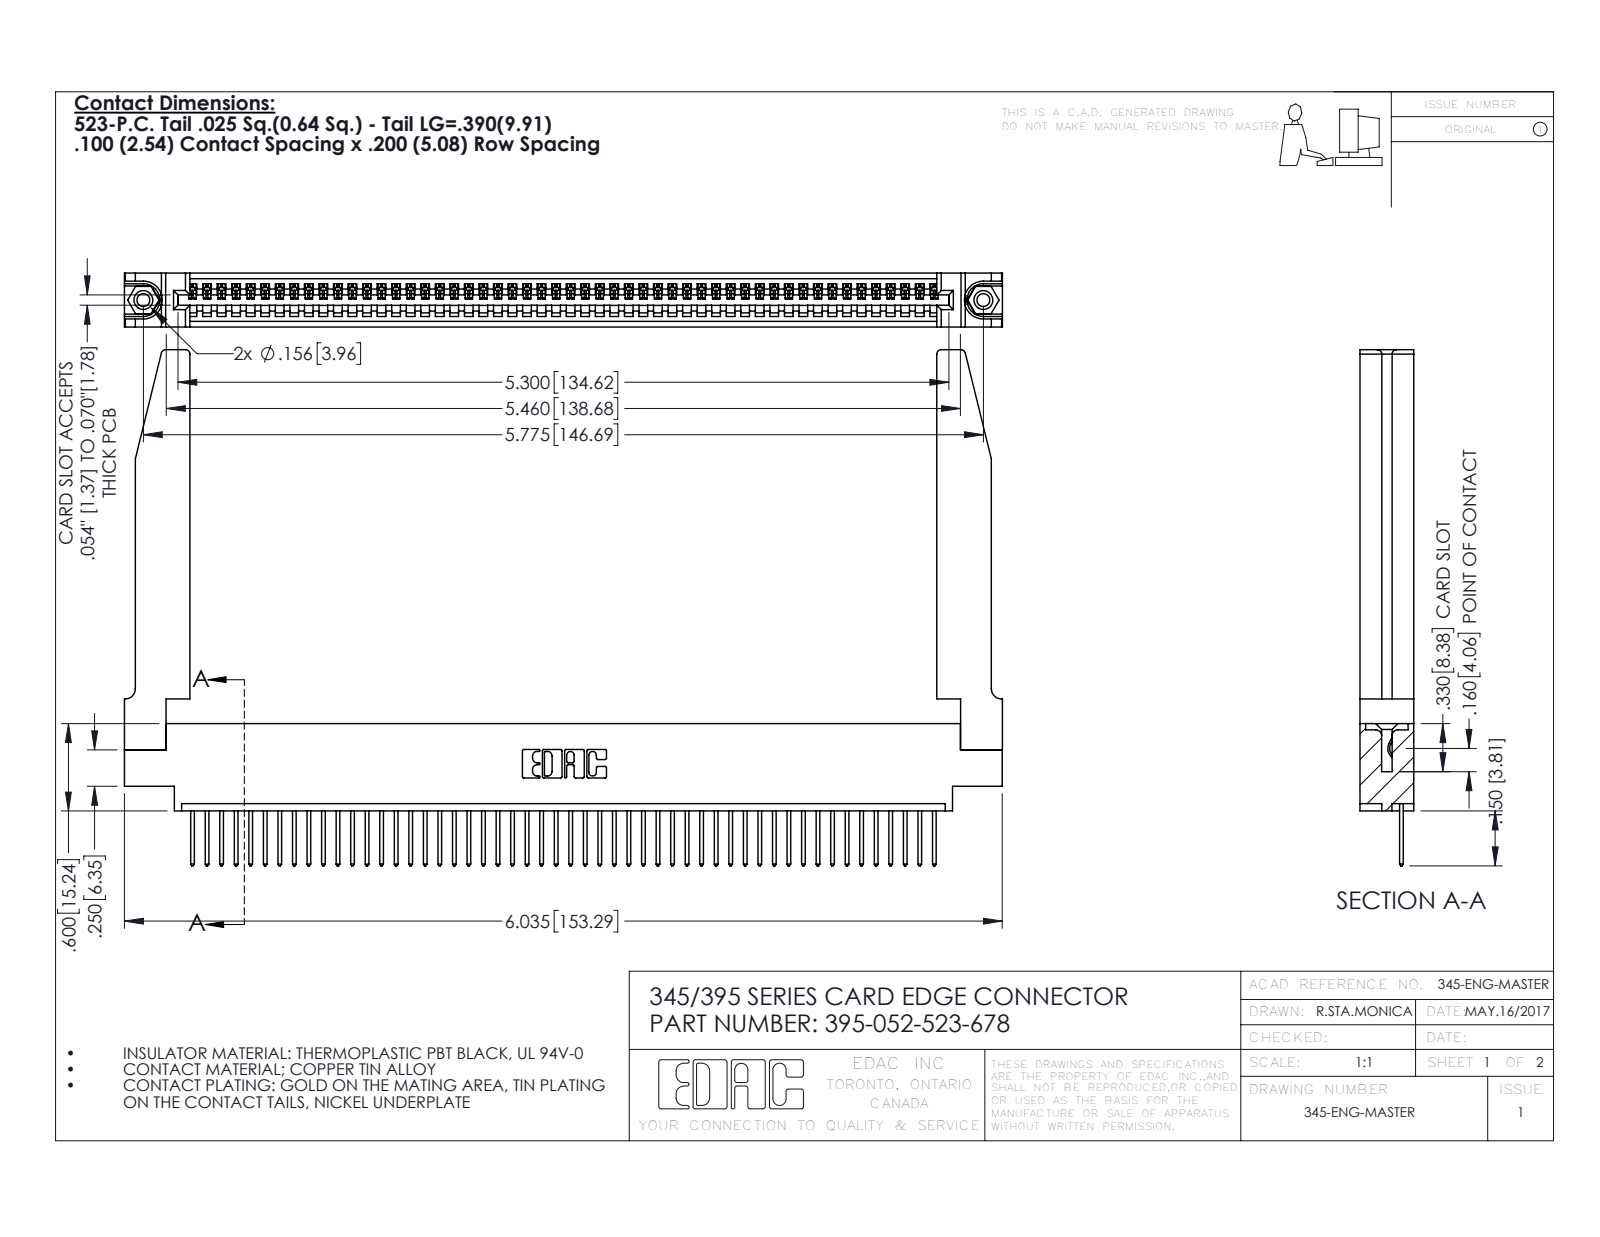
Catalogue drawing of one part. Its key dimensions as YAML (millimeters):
part_name: "395-052-523-678; 345-250-001_345-250-001-102; 345-220-078_345-220-078; 345-292-001_345-293-123 (+1 more)"
step_written_by: "SolidWorks 2016 (CONFIG_CONTROL_DESIGN)"
units: millimeters
bodies: {solids: 57, faces: 3380, planar: 2306, cylindrical: 1022, other: 52}
overall_size: [153.3, 90.1, 9.4]
volume: 22290
surface_area: 26450
round_holes:
  - {diameter: 2.3, count: 2}
  - {diameter: 3.2, count: 2}
  - {diameter: 4, count: 2}
  - {diameter: 1.6, count: 1}
round_bosses_or_shafts:
  - {diameter: 3.9, count: 2}
partial_cylinders:
  - {radius: 0.2, count: 104}
  - {radius: 0.3, count: 104}
  - {radius: 0.3, count: 22}
  - {radius: 0.8, count: 8}
  - {radius: 0.2, count: 6}
  - {radius: 0.8, count: 6}
  - {radius: 0.7, count: 3}
  - {radius: 0.8, count: 2}
face_to_face_distances: [9.4, 1.8, 7.6, 2.5, 6.9, 0.6, 5.1, 5.7, 3.8, 3.8]
hole_center_spacings: [6.9, 140.7, 146.7]
